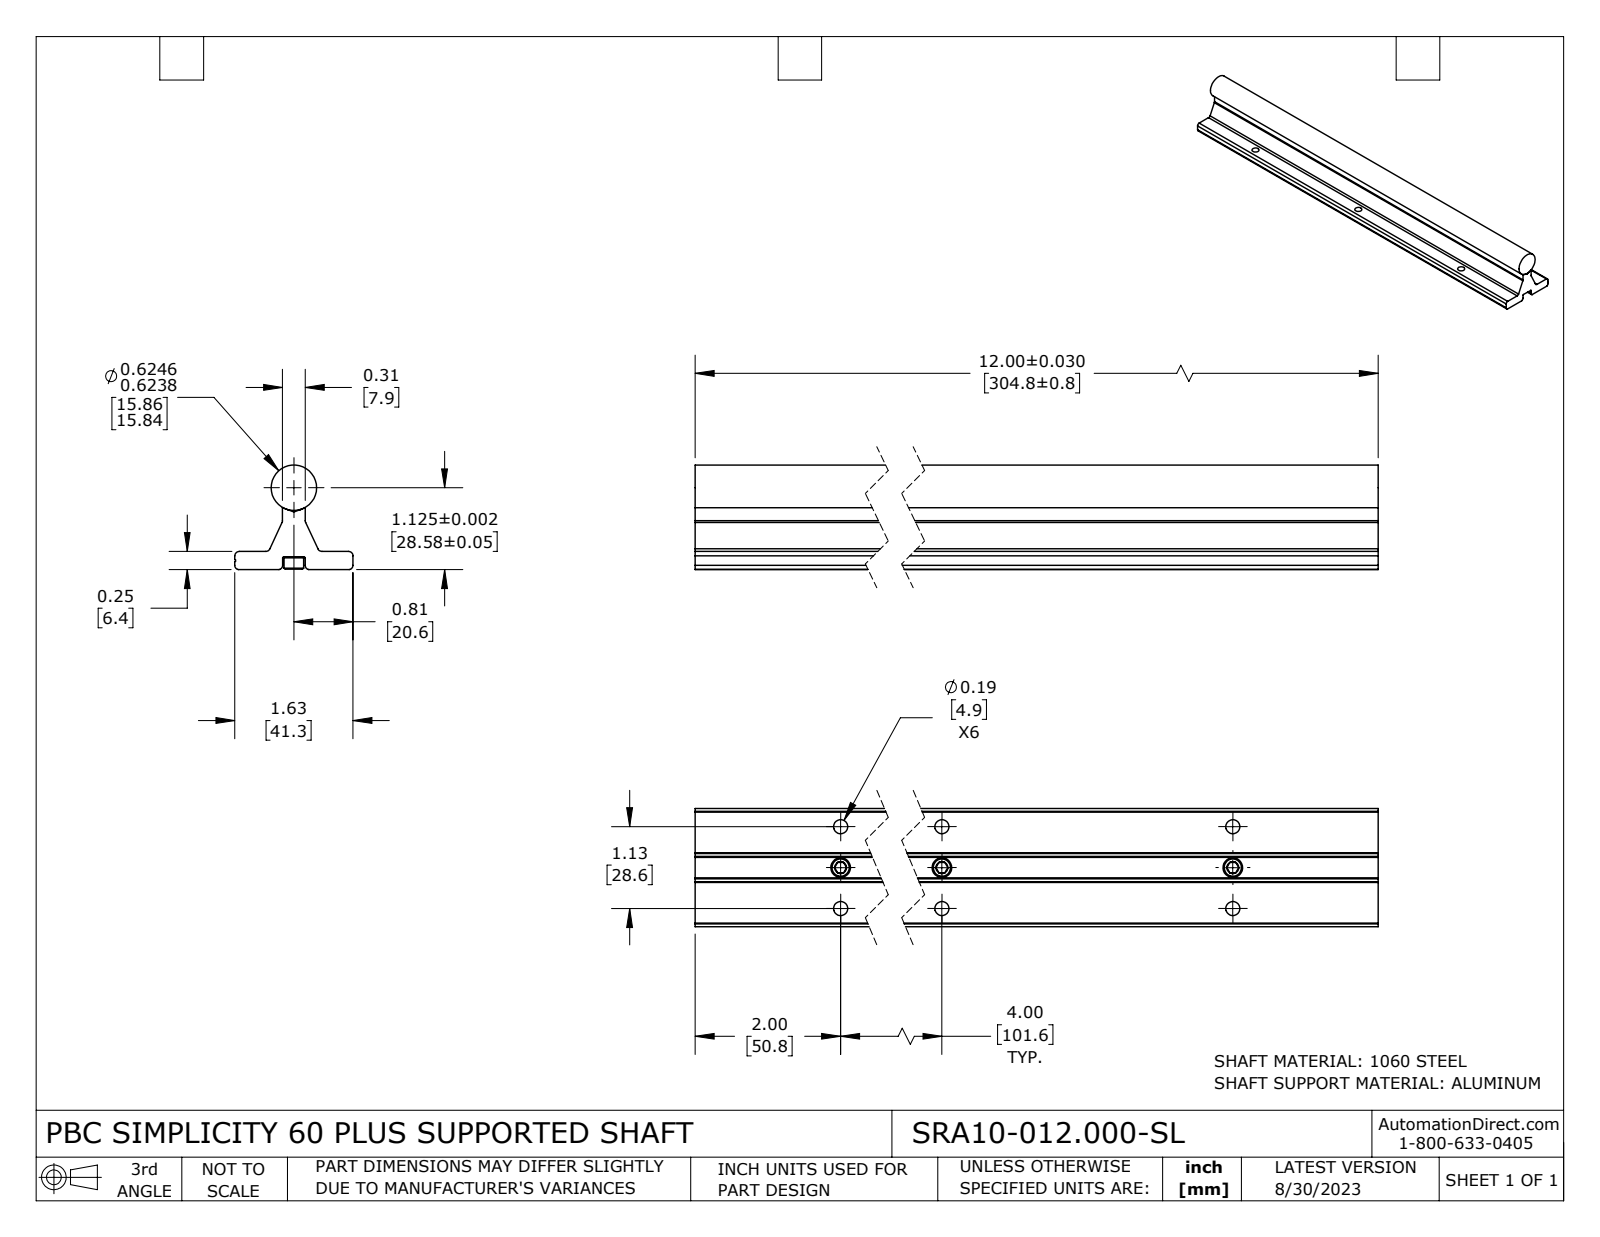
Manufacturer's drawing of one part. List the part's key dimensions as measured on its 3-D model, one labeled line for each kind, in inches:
Part name (STEP PRODUCT): SRA10-012.000-SL
STEP written by: SolidWorks 2021 (CONFIG_CONTROL_DESIGN)
Units: inches
Bodies: 5 solids, 161 faces (60 planar, 56 cylindrical, 45 other)
Overall size (bounding box): 12 × 1.625 × 1.438
Volume: 10.89 in³ · Surface area: 87.98 in²
Round holes (diameter × count): ⌀0.194 ×9, ⌀0.141 ×3, ⌀0.188 ×3
Round bosses / shafts (diameter × count): ⌀0.27 ×3, ⌀0.165 ×3, ⌀0.625 ×1
Partial cylindrical surfaces — rounded edges, fillets, slot ends (radius × count): R0.06 ×6, R0.015 ×2, R0.062 ×2, R0.063 ×2
Main face-to-face distances: 0.25, 0.174, 0.076, 0.656, 0.969, 0.657, 0.968, 0.311, 0.313, 1.625
Hole centre spacings: 4.039, 0.563, 4, 4.155, 8.02, 1.125, 8, 8.079
